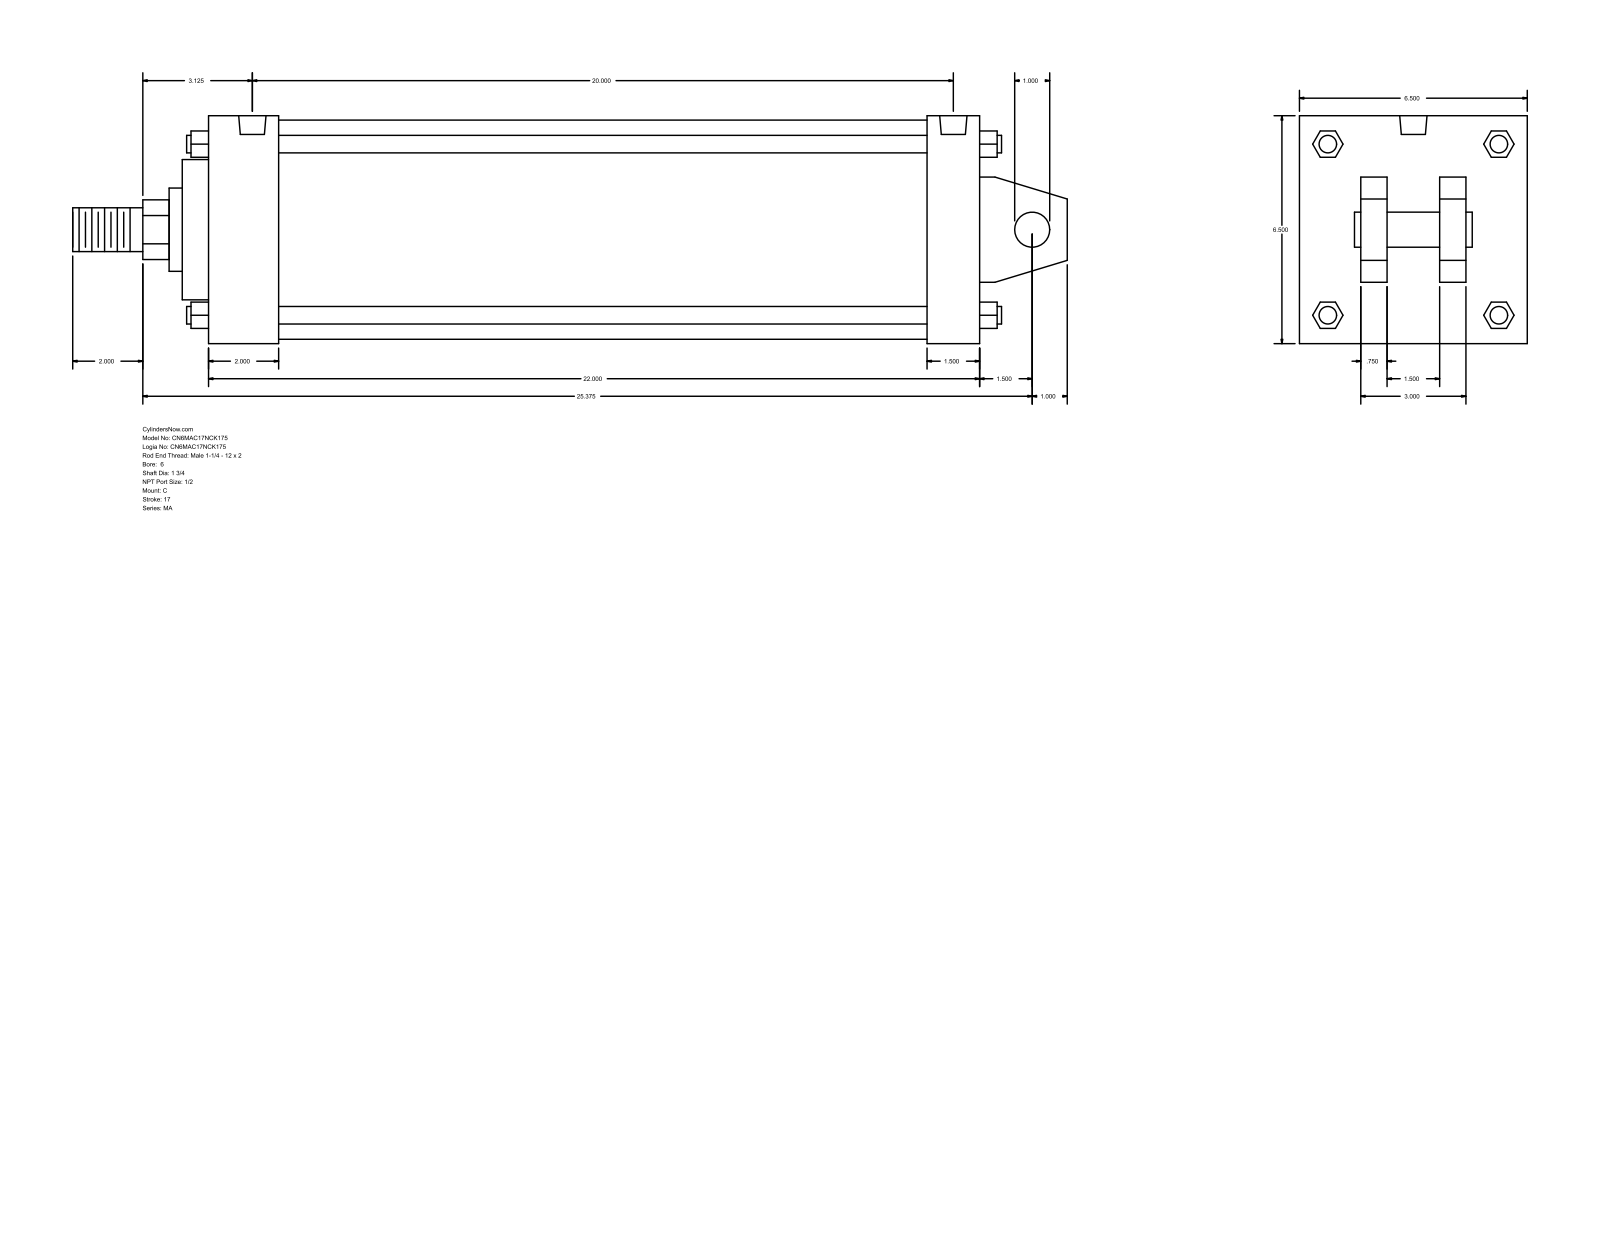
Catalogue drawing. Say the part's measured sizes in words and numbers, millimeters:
The part is named "MA_C__0600_1.75". Its 3-D file was written by "GSSL Pune (CONFIG_CONTROL_DESIGN)". It is 0 solids with 141 faces: 109 planar, 32 cylindrical and 0 other. Overall it measures 720.73 by 165.1 by 165.1 millimeters. Round holes: 4 of diameter 17.46, 2 of diameter 19.77. Round bosses or shafts: 4 of diameter 12.7, 1 of diameter 158.75, 1 of diameter 101.6, 1 of diameter 60.33, 1 of diameter 44.45, 1 of diameter 31.75, 1 of diameter 25.4. Partial cylindrical surfaces (rounded edges, fillets, slot ends): 1 of radius 21.63. The main face-to-face distances are 165.1, 558.8, 19.05, 63.5, 101.6, 50.8, 44.45, 120.65, 57.15, 508. The hole center spacings are 508.
